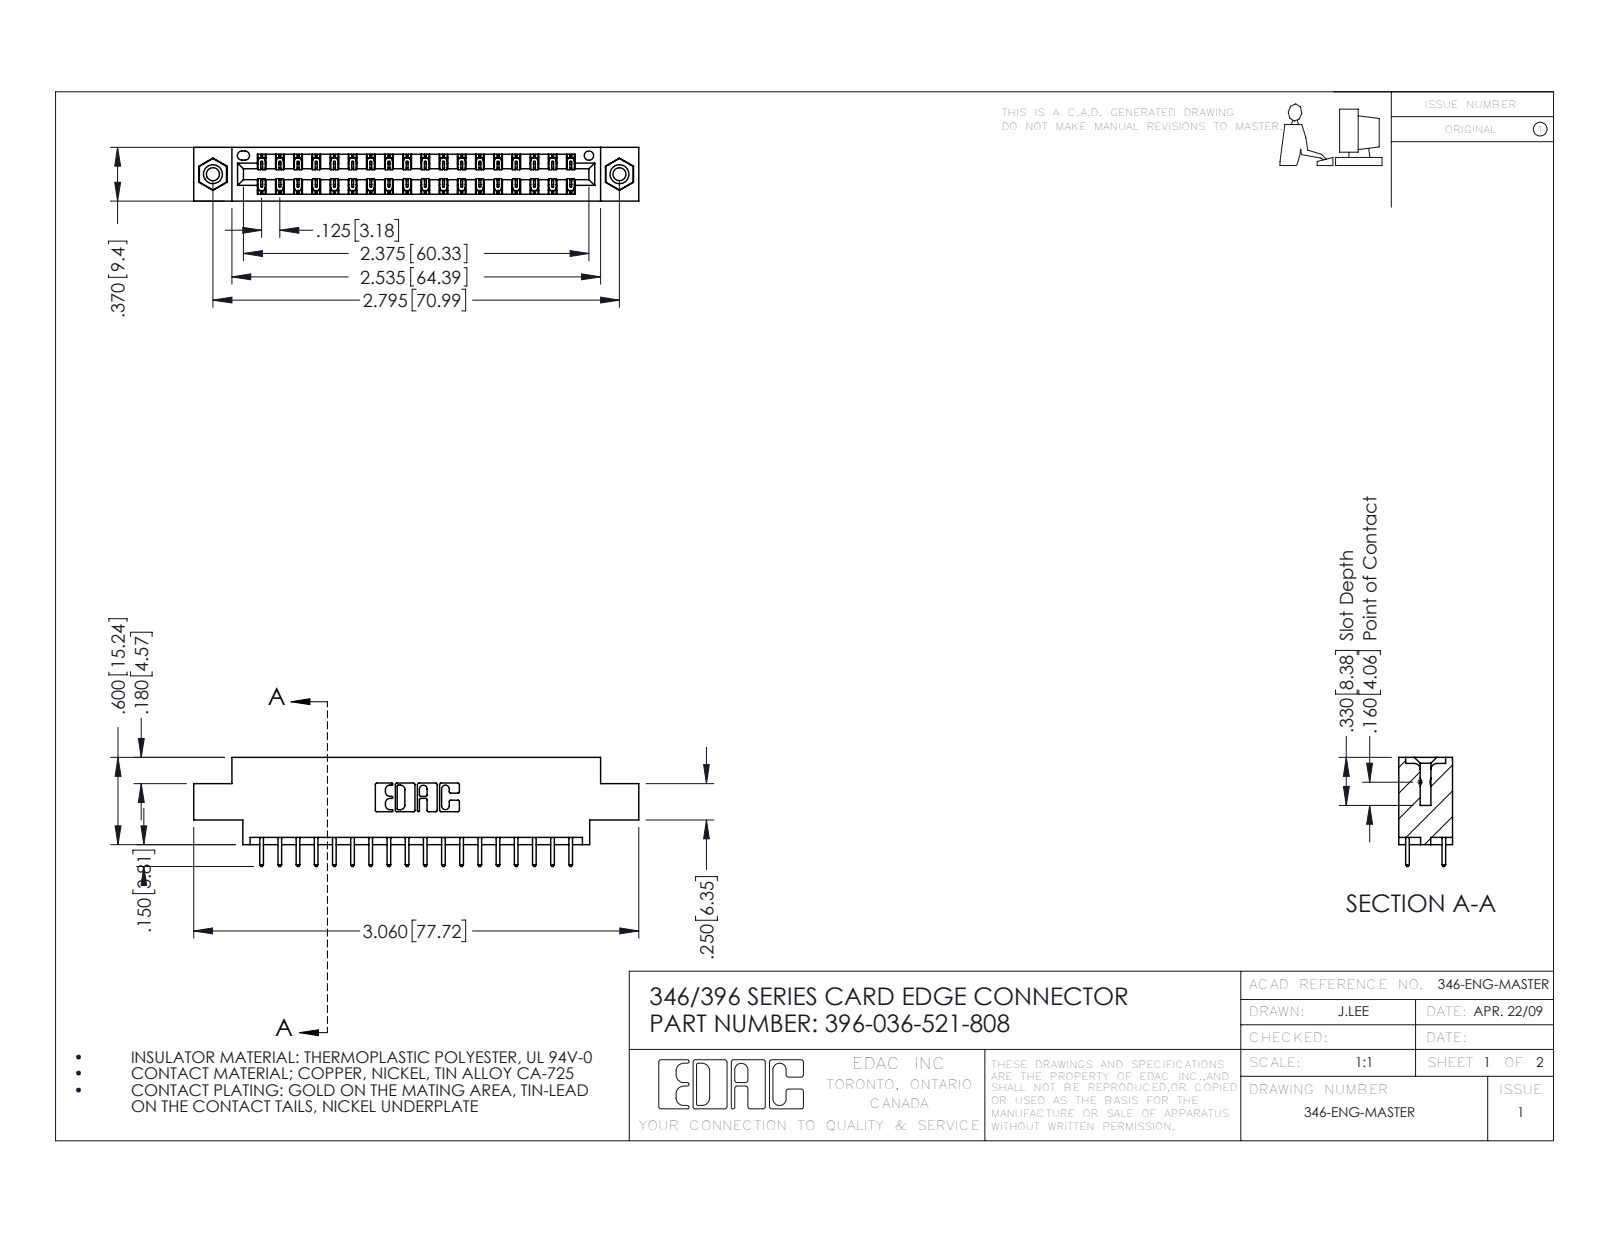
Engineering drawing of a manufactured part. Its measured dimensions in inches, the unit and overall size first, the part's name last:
Units: inches
Overall size (bounding box): 3.06 × 0.75 × 0.37
Round holes (diameter × count): ⌀0.089 ×2, ⌀0.125 ×2, ⌀0.156 ×2, ⌀0.064 ×1
Round bosses / shafts (diameter × count): ⌀0.155 ×2
Partial cylindrical surfaces — rounded edges, fillets, slot ends (radius × count): R0.006 ×54, R0.01 ×36, R0.01 ×22, R0.007 ×6, R0.031 ×6, R0.026 ×3, R0.014 ×2, R0.022 ×2
Main face-to-face distances: 0.048, 0.322, 0.25, 0.37, 0.072, 0.298, 0.025, 0.275, 0.222, 0.148
Hole centre spacings: 0.246, 2.588, 2.795
Volume: 0.44 in³ · Surface area: 14.95 in²
Bodies: 39 solids, 2058 faces (1372 planar, 670 cylindrical, 16 other)
Part name (STEP PRODUCT): 396-036-521-808; 345-292-001_345-293-121; 345-250-001_345-250-003-102; 346 Part_0.170 Offset - 0.156 Dia-TI
STEP written by: SolidWorks 2016 (CONFIG_CONTROL_DESIGN)
